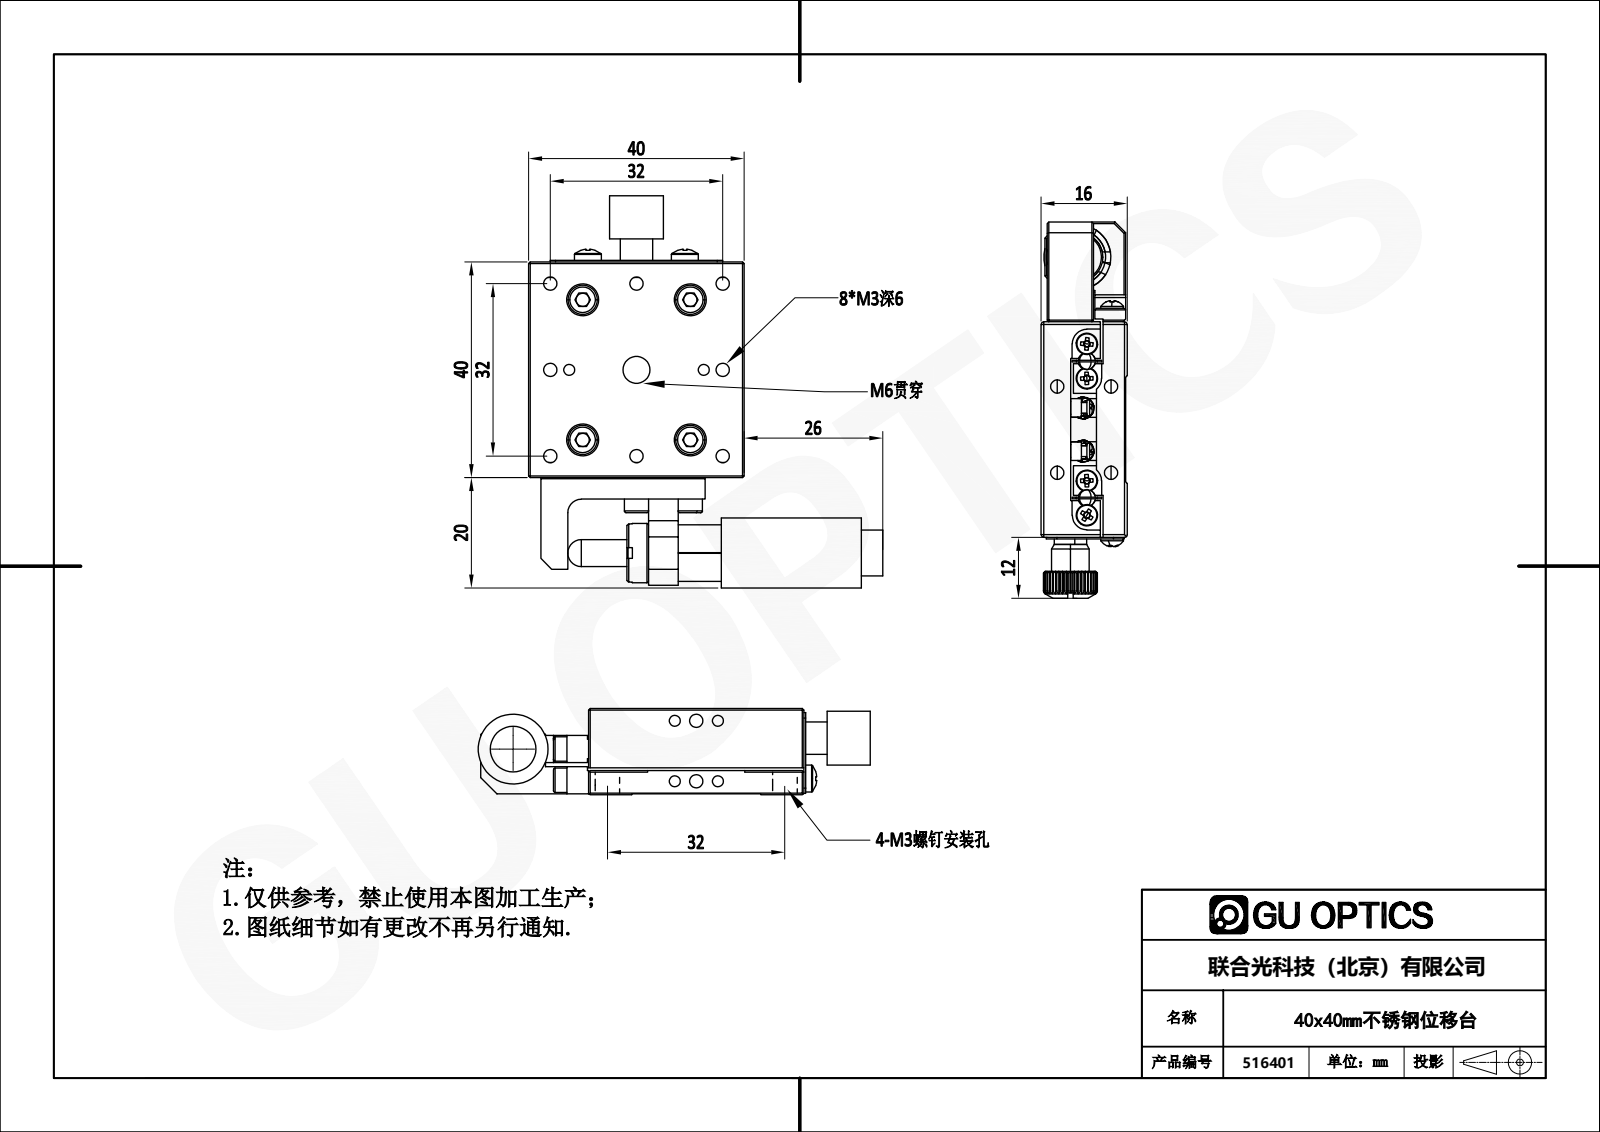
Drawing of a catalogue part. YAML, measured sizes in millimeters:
part_name: "TSS416-05L"
step_written_by: "SolidWorks 2020 (CONFIG_CONTROL_DESIGN)"
units: millimeters
bodies: {solids: 26, faces: 493, planar: 320, cylindrical: 109, other: 64}
overall_size: [72.8, 65.75, 16]
volume: 31572
surface_area: 17586
round_holes:
  - {diameter: 2.05, count: 14}
  - {diameter: 2.5, count: 12}
  - {diameter: 6, count: 8}
  - {diameter: 3, count: 6}
  - {diameter: 1.6, count: 4}
  - {diameter: 2.7, count: 4}
  - {diameter: 3.4, count: 4}
  - {diameter: 5, count: 1}
  - {diameter: 9, count: 1}
round_bosses_or_shafts:
  - {diameter: 2.5, count: 7}
  - {diameter: 5.5, count: 4}
  - {diameter: 4.5, count: 4}
  - {diameter: 3.4, count: 4}
  - {diameter: 2, count: 4}
  - {diameter: 5, count: 3}
  - {diameter: 13, count: 1}
  - {diameter: 11, count: 1}
partial_cylinders:
  - {radius: 1, count: 4}
  - {radius: 1.75, count: 2}
  - {radius: 2.5, count: 1}
face_to_face_distances: [11, 4.3, 4.8, 0.5, 15.8, 11.5, 40, 5, 4, 40.3]
hole_center_spacings: [16, 11.66, 20, 19, 22.63, 35.78, 32, 4]
